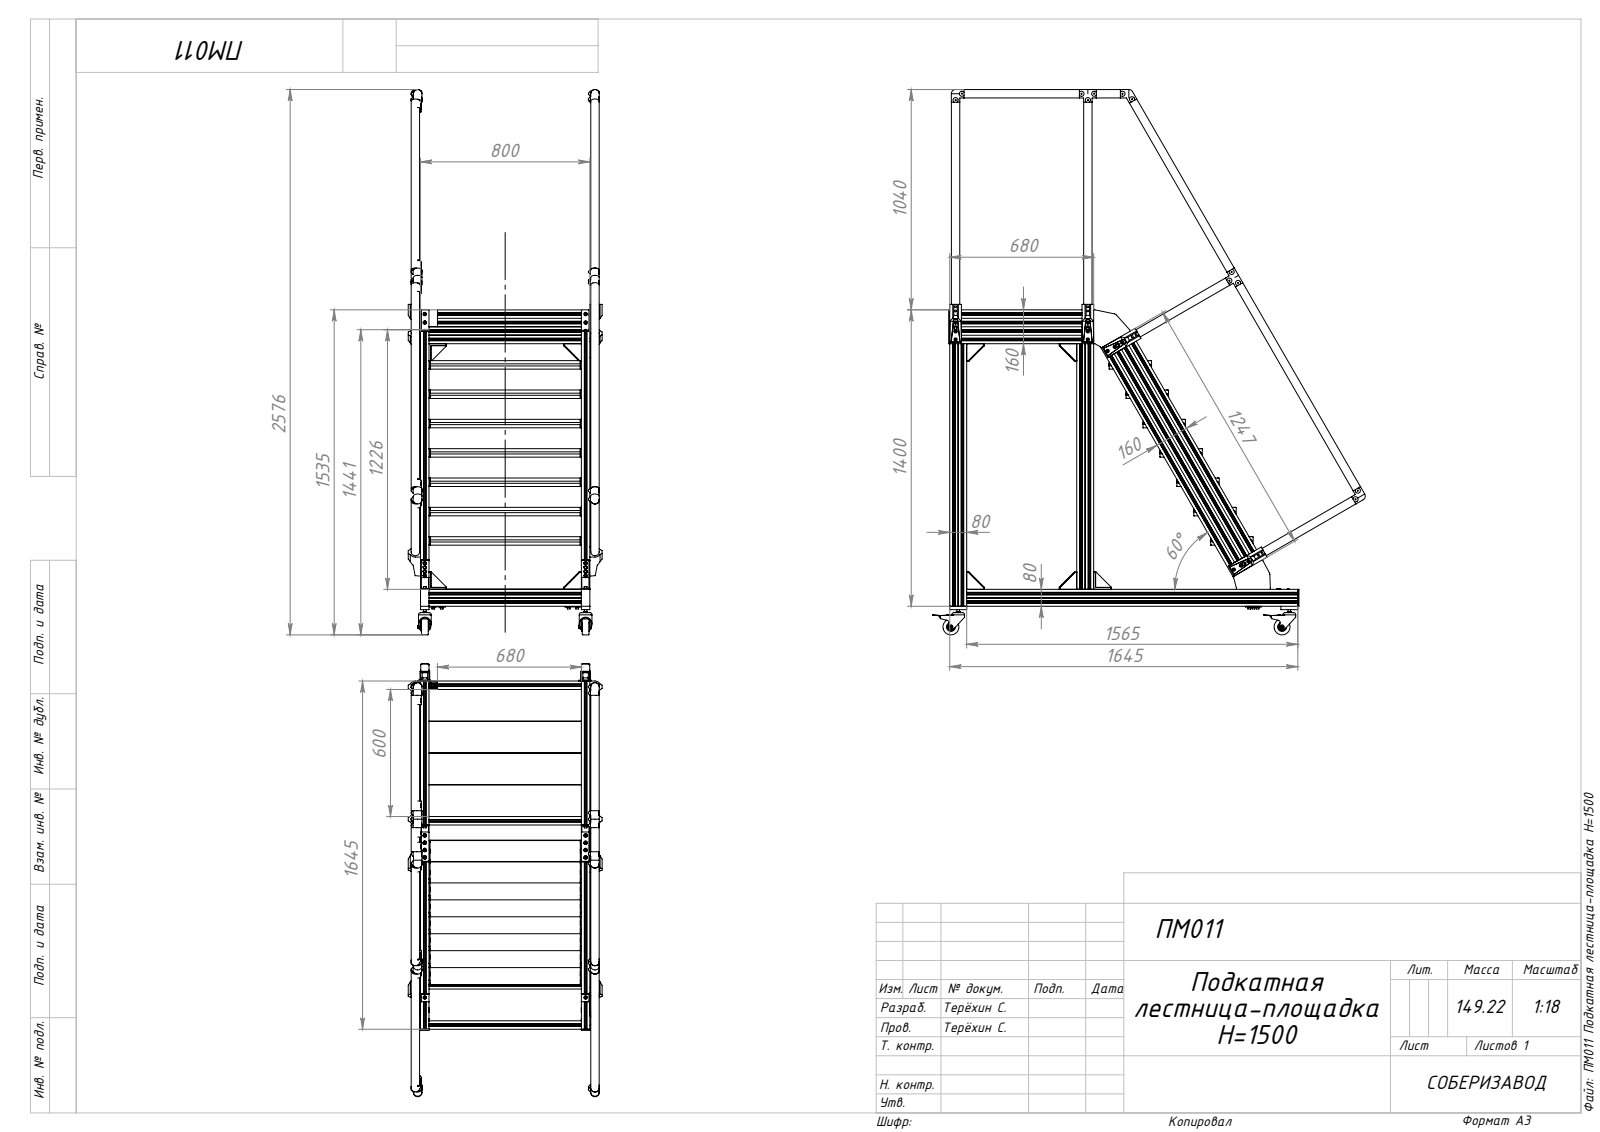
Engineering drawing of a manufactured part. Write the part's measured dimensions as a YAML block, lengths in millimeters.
part_name: "D72; D10_00; 448 Конструкционный профиль 40х80_3; SNSK.17.00.01.ФиксаторV40_tupe1 (+8 more)"
step_written_by: "SolidWorks 2026 (AUTOMOTIVE_DESIGN)"
units: millimeters
bodies: {solids: 710, faces: 41010, planar: 18736, cylindrical: 13958, other: 8316}
overall_size: [2575.53, 2044.58, 916]
volume: 42820000
surface_area: 29140000
round_holes:
  - {diameter: 8.4, count: 85}
  - {diameter: 6.7, count: 66}
  - {diameter: 7, count: 66}
  - {diameter: 9, count: 60}
  - {diameter: 9.2, count: 49}
  - {diameter: 8, count: 21}
  - {diameter: 23.4, count: 18}
  - {diameter: 26, count: 18}
  - {diameter: 14, count: 16}
  - {diameter: 8.2, count: 15}
  - {diameter: 33.6, count: 14}
  - {diameter: 7.4, count: 9}
round_bosses_or_shafts:
  - {diameter: 13, count: 96}
  - {diameter: 8, count: 96}
  - {diameter: 16, count: 77}
  - {diameter: 14, count: 28}
  - {diameter: 33.5, count: 18}
  - {diameter: 30.4, count: 18}
  - {diameter: 26.4, count: 18}
  - {diameter: 40, count: 16}
partial_cylinders:
  - {radius: 0.25, count: 1786}
  - {radius: 1, count: 1326}
  - {radius: 0.5, count: 821}
  - {radius: 0.3, count: 702}
  - {radius: 0.1, count: 658}
  - {radius: 0.4, count: 636}
  - {radius: 0.2, count: 616}
  - {radius: 2, count: 430}
face_to_face_distances: [40, 760, 29, 11, 18, 7, 4, 25, 36, 720]
hole_center_spacings: [760, 761.05, 40, 837.6, 764.2, 80, 848.6, 11]
